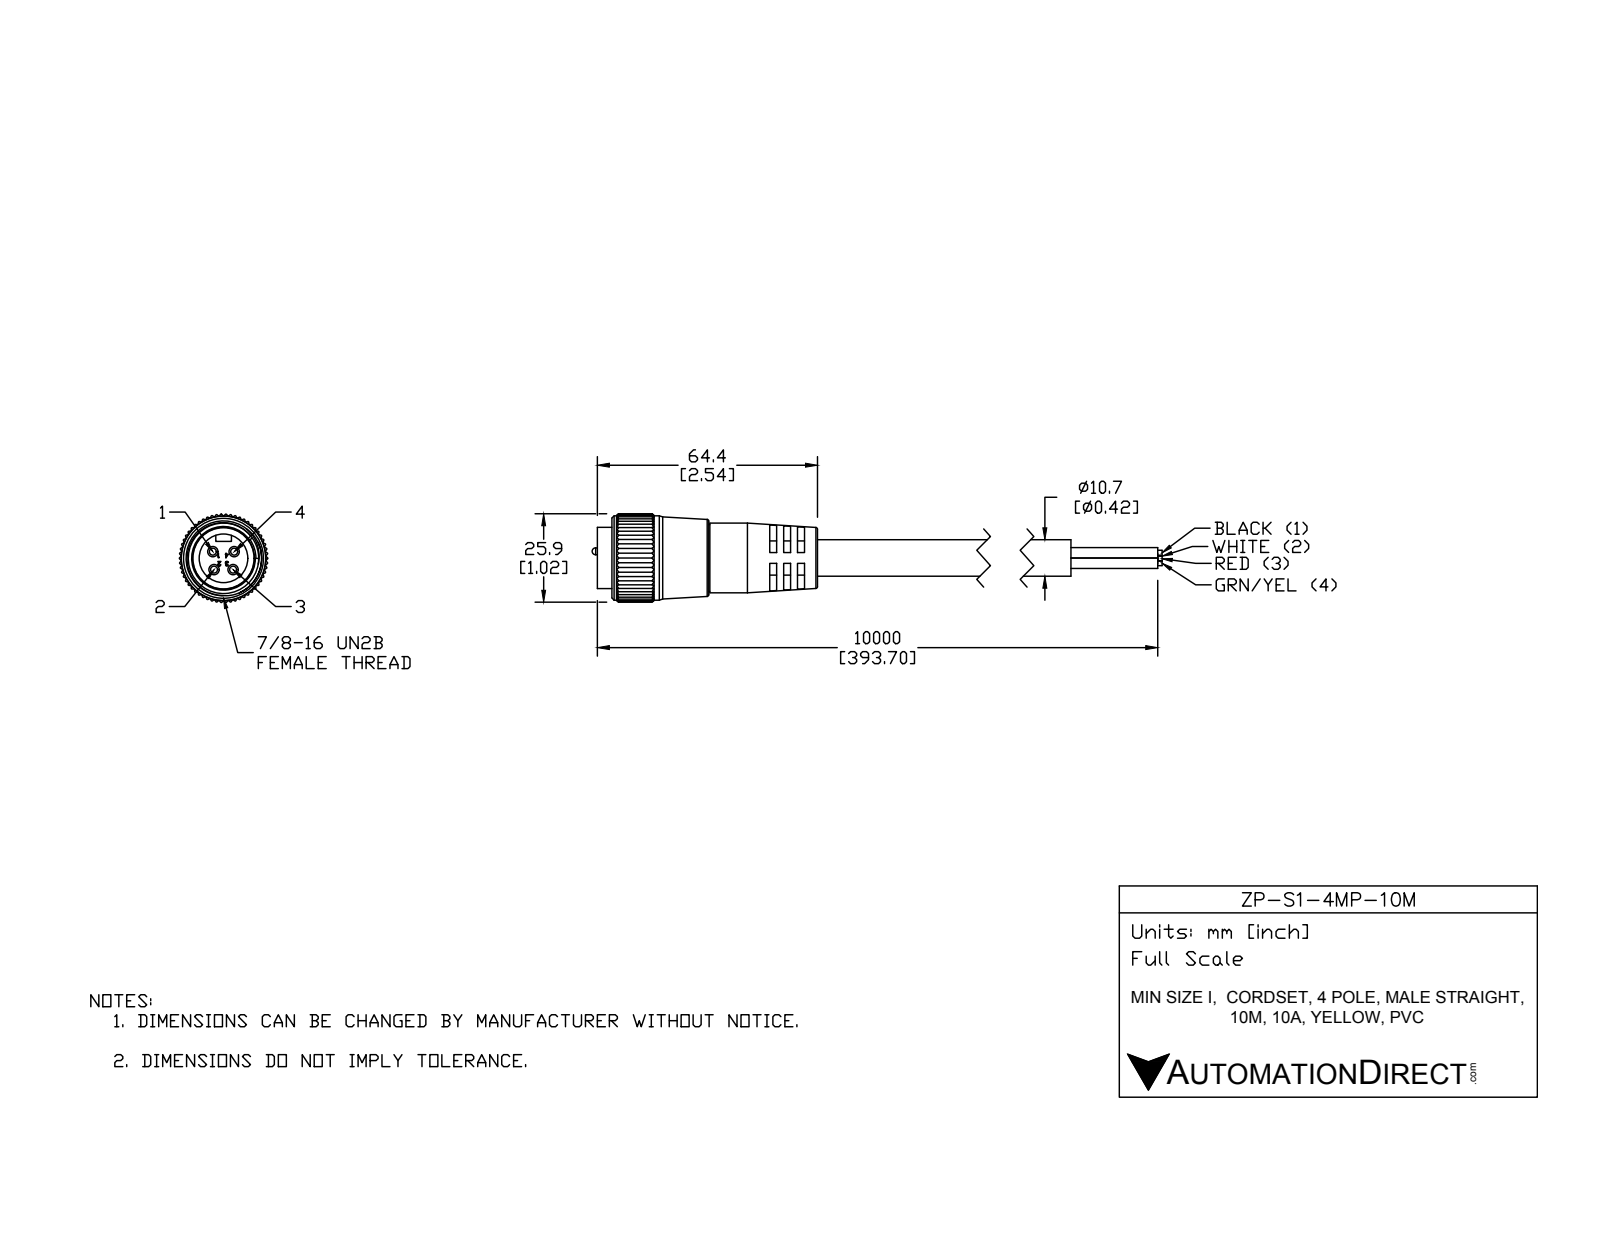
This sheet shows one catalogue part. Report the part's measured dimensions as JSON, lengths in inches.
{"part_name": "ZP-S1-4MP-10M", "step_written_by": "SolidWorks 2015 (AUTOMOTIVE_DESIGN)", "units": "inches", "bodies": {"solids": 6, "faces": 589, "planar": 213, "cylindrical": 318, "other": 58}, "overall_size": [4.331, 2.083, 1.017], "volume_in3": 1.704, "surface_area_in2": 19.89, "round_holes": [[0.56, 1], [0.786, 1], [0.805, 1], [0.827, 1]], "round_bosses_or_shafts": [[0.12, 4], [0.079, 4], [0.42, 2], [0.972, 1], [0.803, 1], [0.768, 1], [0.704, 1]], "partial_cylinders_radius": [[0.01, 165], [0.09, 1], [0.207, 1], [0.509, 1]], "face_to_face_distances": [0.079, 0.159, 0.08, 0.238, 0.546, 0.468, 0.387, 0.309, 0.229, 0.317]}
